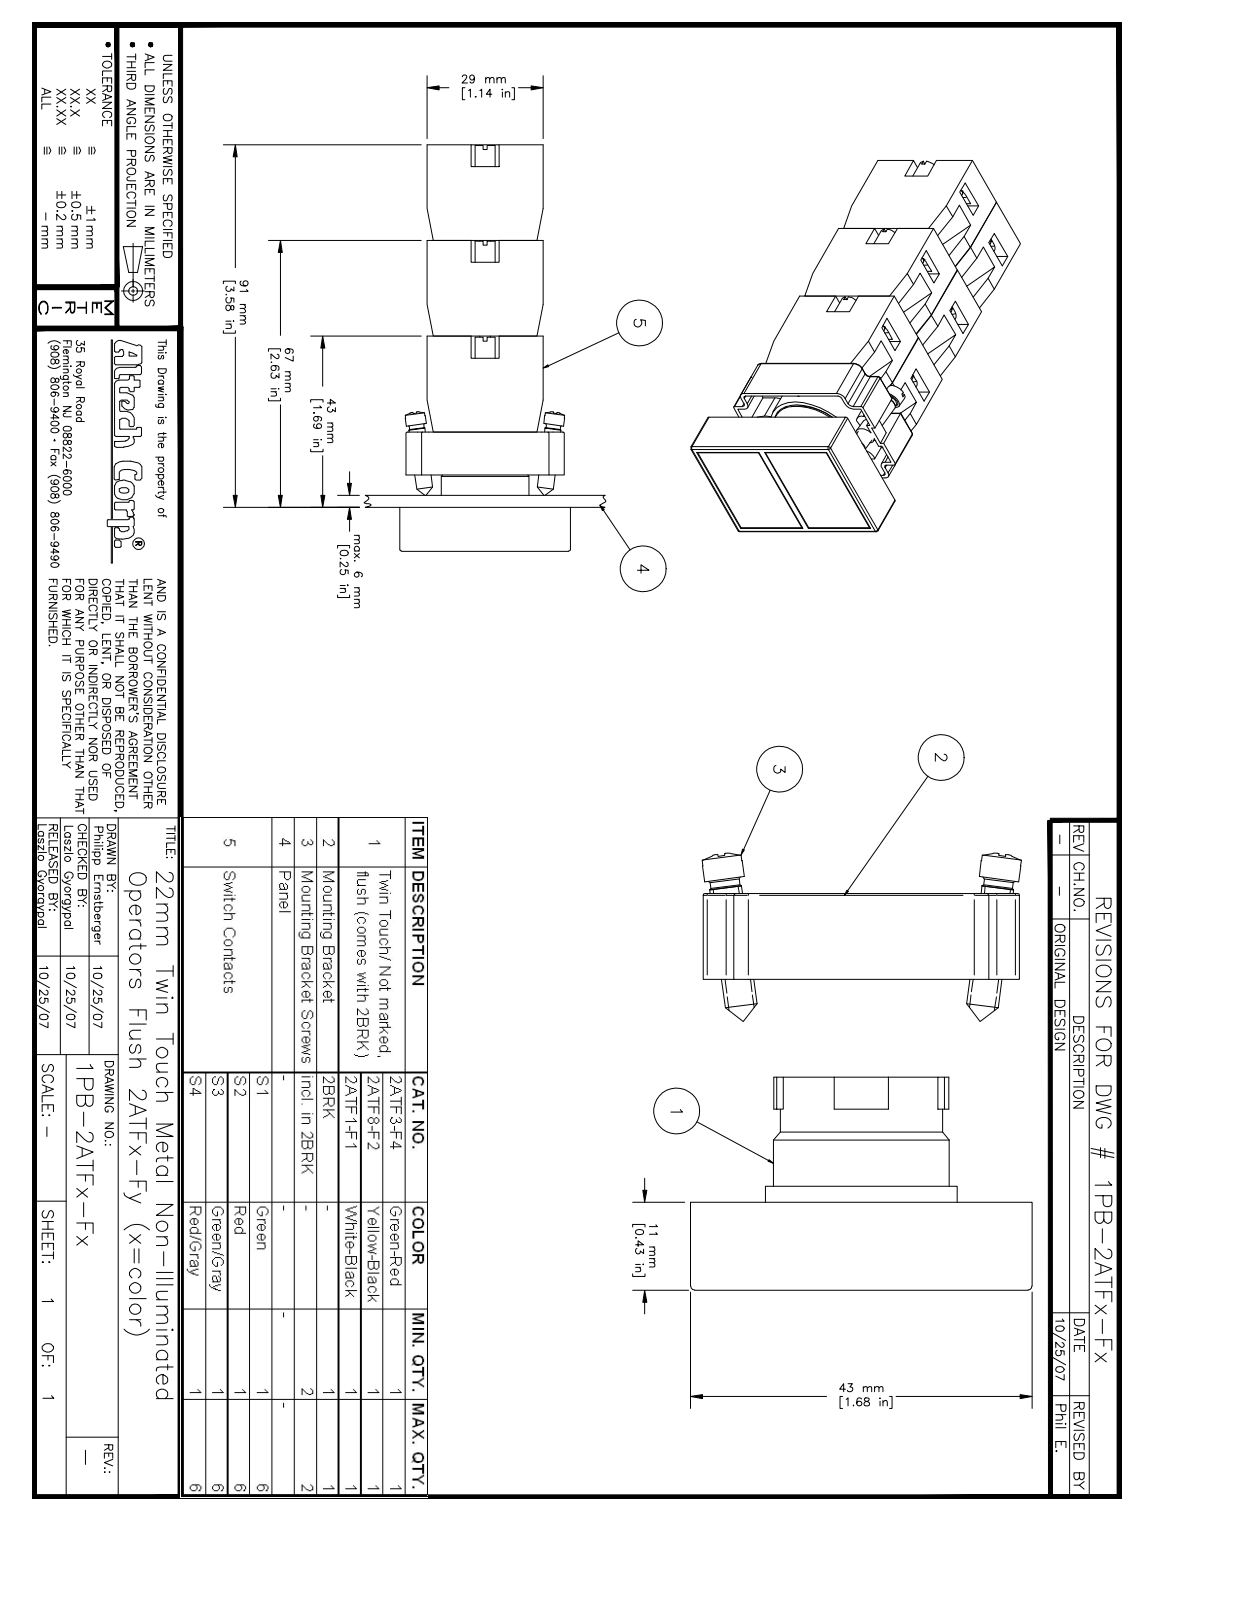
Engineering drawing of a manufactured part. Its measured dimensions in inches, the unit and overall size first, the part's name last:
Units: inches
Overall size (bounding box): 4.012 × 2.38 × 1.772
Round holes (diameter × count): ⌀0.098 ×5, ⌀0.102 ×2, ⌀0.866 ×1, ⌀0.876 ×1, ⌀0.886 ×1
Round bosses / shafts (diameter × count): ⌀0.118 ×6, ⌀0.197 ×4, ⌀0.108 ×4, ⌀0.059 ×4, ⌀0.157 ×2, ⌀0.144 ×2, ⌀0.955 ×1, ⌀0.945 ×1
Partial cylindrical surfaces — rounded edges, fillets, slot ends (radius × count): R0.039 ×13, R0.02 ×12, R0.01 ×11, R0.028 ×8, R0.089 ×5, R0.031 ×4, R0.071 ×4, R0.079 ×4
Main face-to-face distances: 0.583, 0.579, 0.945, 0.118, 1.161, 1.89, 1.142, 0.433, 0.551, 2.516
Hole centre spacings: 0.572, 0.257, 0.259, 0.512, 1.019, 1.024, 1.034, 1.144
Volume: 4.969 in³ · Surface area: 74.66 in²
Bodies: 30 solids, 1234 faces (684 planar, 193 cylindrical, 357 other)
Part name (STEP PRODUCT): 2ATFx-Fx_assembly; 2BRK; DIN 7985 (Z) M4x18-Z; S1 (+7 more)
STEP written by: Autodesk Inventor 2008 (AUTOMOTIVE_DESIGN)
